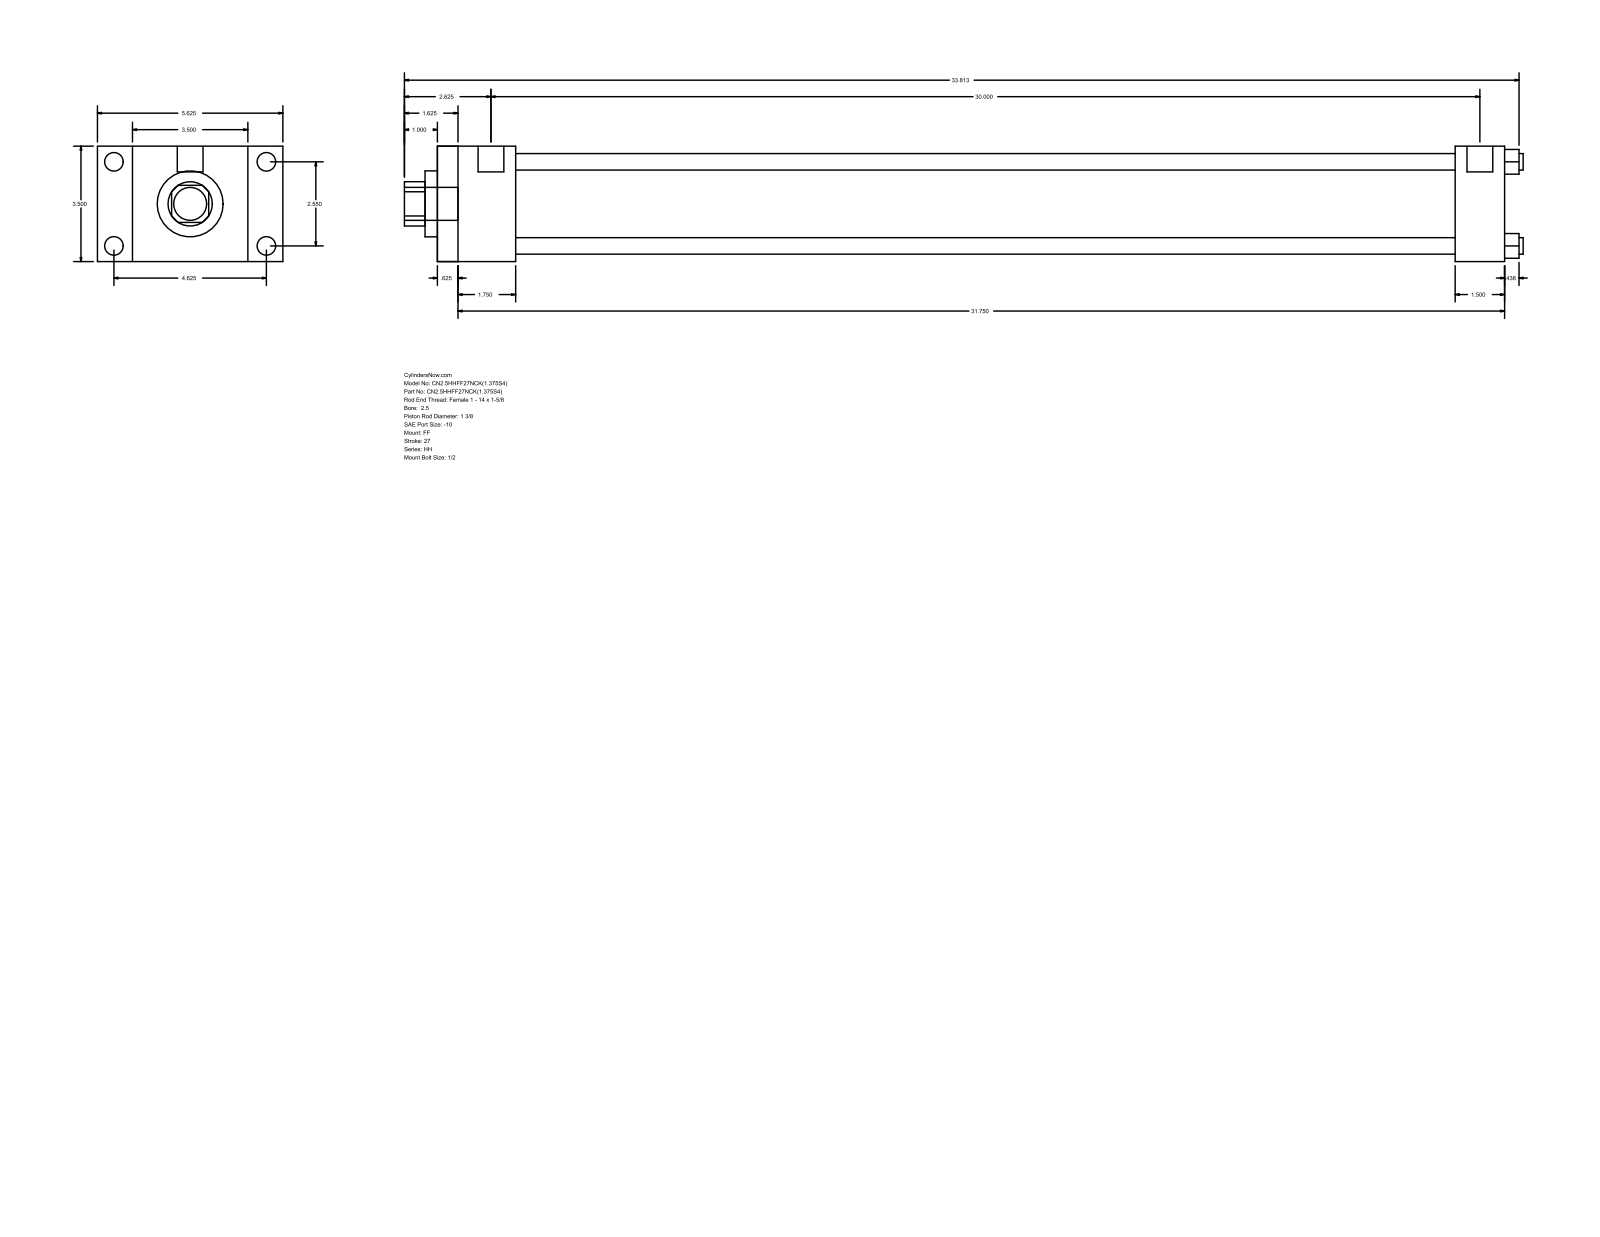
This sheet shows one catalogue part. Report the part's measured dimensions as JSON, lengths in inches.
{"part_name": "HH_FF__0250_1.375", "step_written_by": "GSSL Pune (CONFIG_CONTROL_DESIGN)", "units": "inches", "bodies": {"solids": 0, "faces": 92, "planar": 64, "cylindrical": 28, "other": 0}, "overall_size": [33.937, 5.625, 3.5], "round_holes": [[0.5, 4], [1.375, 1], [2, 1], [2.875, 1]], "round_bosses_or_shafts": [[0.563, 4], [0.219, 4], [0.781, 2], [1, 1]], "partial_cylinders_radius": [[0.672, 1]], "face_to_face_distances": [3.5, 32.375, 0.625, 31.75, 2.375, 1.75, 30, 30.875, 30.25, 28.5], "hole_center_spacings": [1.803, 2.55, 3.606]}
